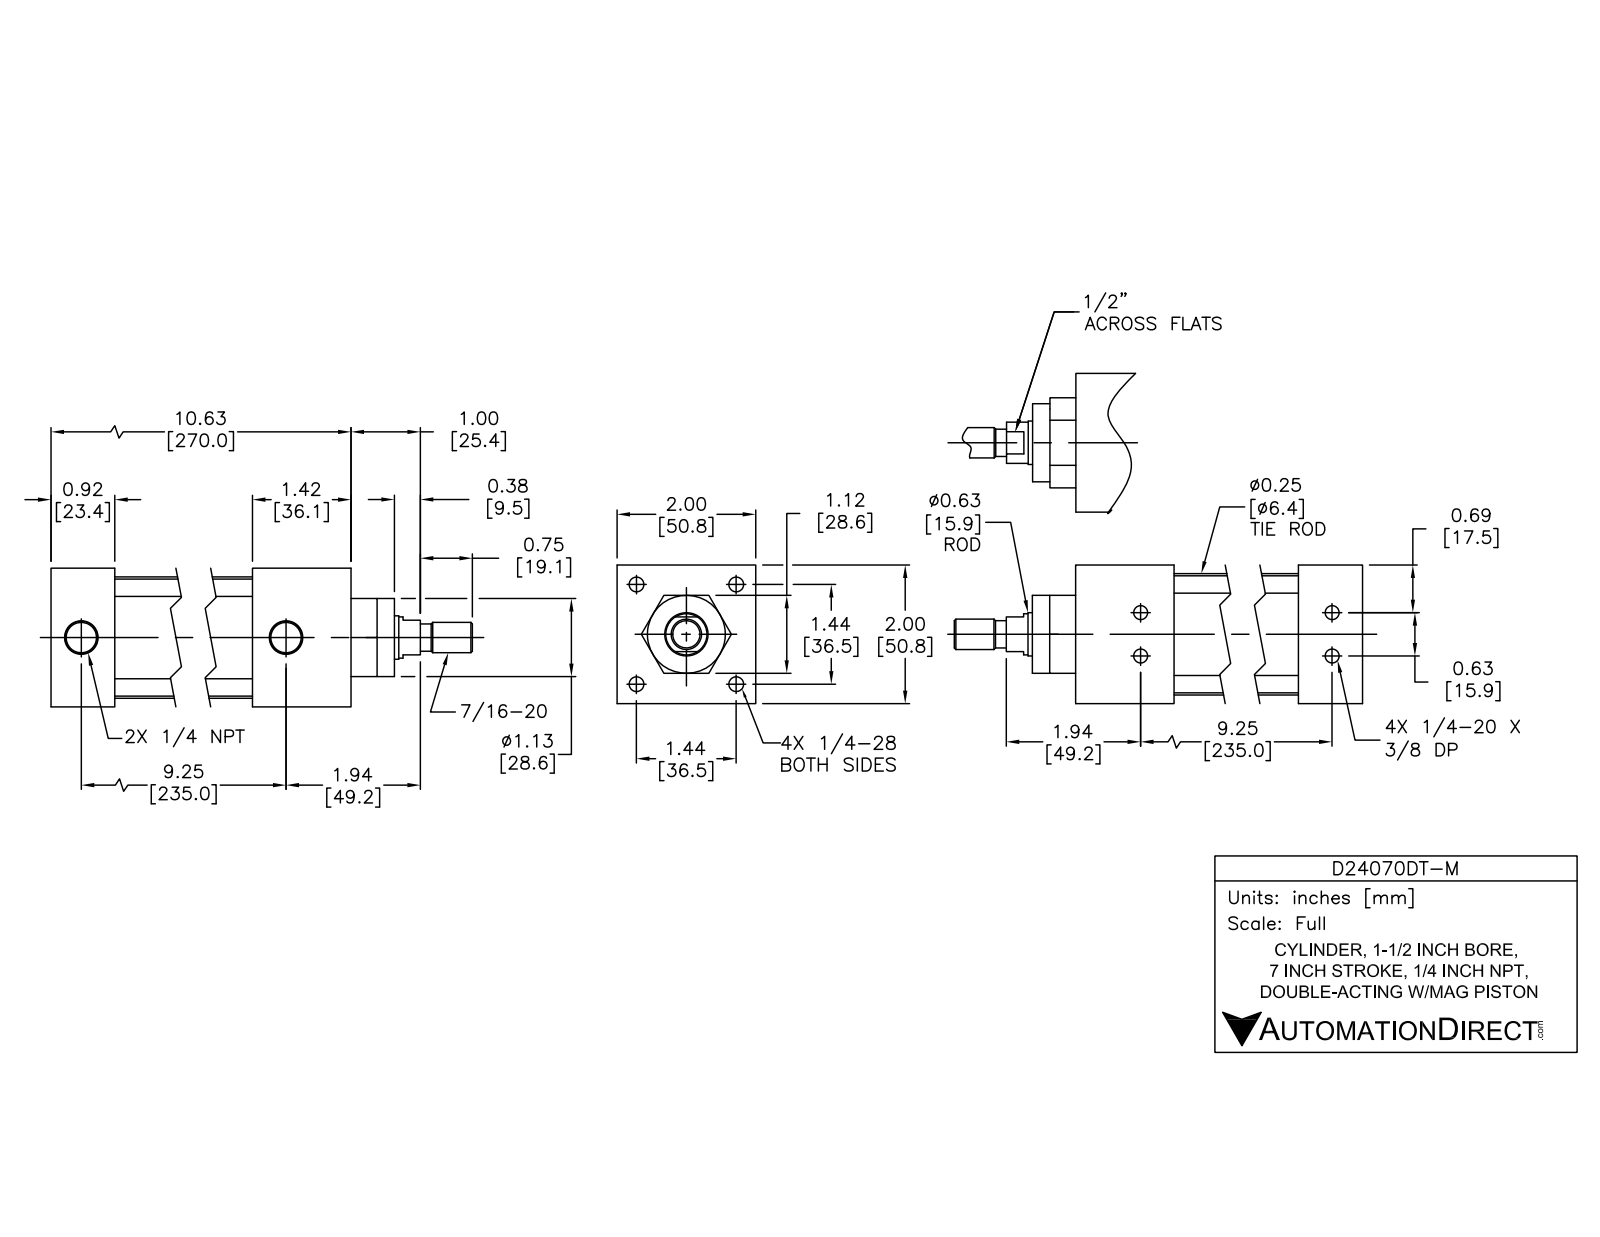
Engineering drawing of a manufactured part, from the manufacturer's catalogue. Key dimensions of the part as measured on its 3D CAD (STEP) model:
Part name (STEP PRODUCT): D24070DT-M PISTON; D24070DT-M BODY; D24070DT-M
STEP written by: SolidWorks 2015 (AUTOMOTIVE_DESIGN)
Units: inches
Bodies: 12 solids, 303 faces (99 planar, 114 cylindrical, 90 other)
Overall size (bounding box): 12.371 × 2 × 2
Volume: 20.37 in³ · Surface area: 197.7 in²
Round holes (diameter × count): ⌀0.196 ×4, ⌀0.211 ×4, ⌀0.281 ×4, ⌀0.406 ×4, ⌀0.297 ×2, ⌀0.477 ×2, ⌀0.625 ×1, ⌀0.628 ×1, ⌀1.5 ×1
Round bosses / shafts (diameter × count): ⌀0.39 ×4, ⌀0.25 ×4, ⌀0.222 ×4, ⌀1.75 ×1, ⌀1.497 ×1, ⌀1.121 ×1, ⌀0.622 ×1, ⌀0.59 ×1
Partial cylindrical surfaces — rounded edges, fillets, slot ends (radius × count): R0.2 ×4
Main face-to-face distances: 2, 10.621, 1.42, 9.201, 9.701, 8.281, 0.92, 1.121, 9.601, 8.181
Hole centre spacings: 0.313, 1.014, 1.434, 0.625, 2.028, 9.247, 9.251, 9.251
